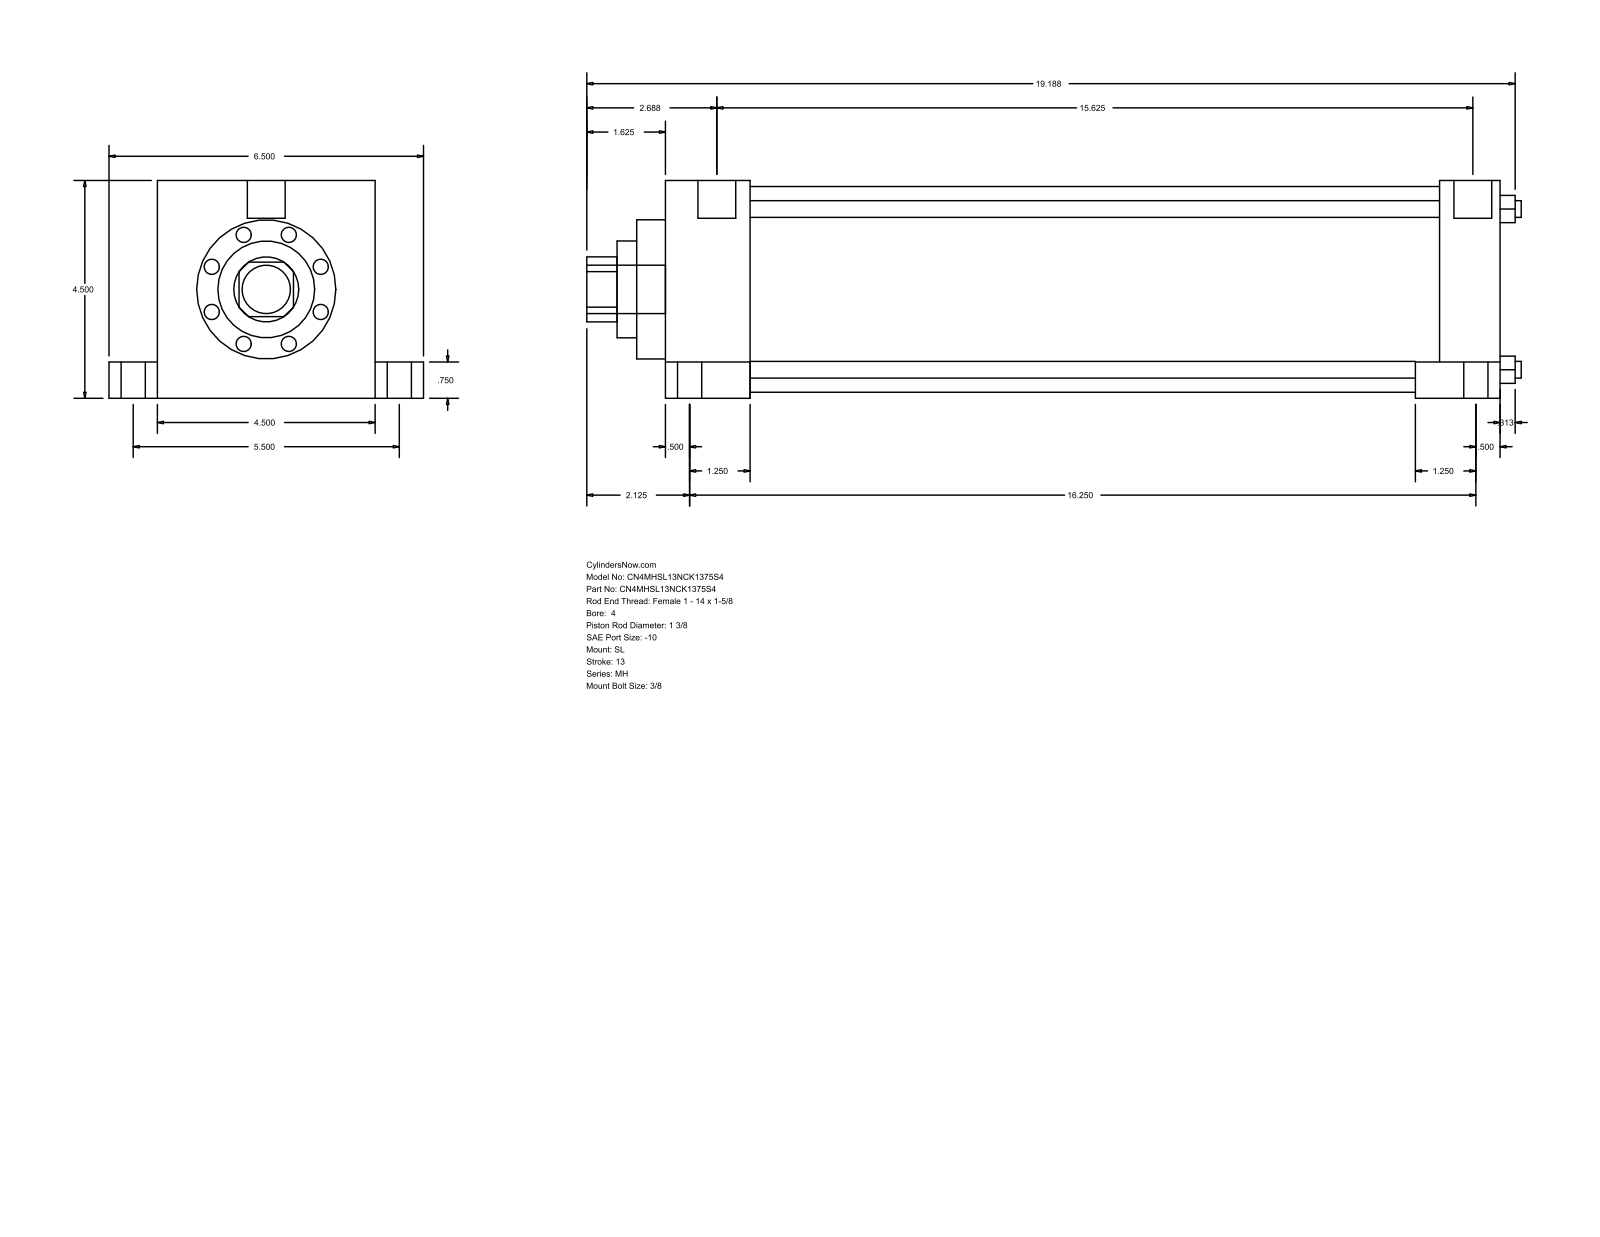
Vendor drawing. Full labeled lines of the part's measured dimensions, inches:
Part name (STEP PRODUCT): MH_SL__0400_1.375
STEP written by: GSSL Pune (CONFIG_CONTROL_DESIGN)
Units: inches
Bodies: 0 solids, 110 faces (77 planar, 33 cylindrical, 0 other)
Overall size (bounding box): 19.313 × 6.5 × 4.5
Round holes (diameter × count): ⌀0.345 ×4, ⌀1.375 ×1, ⌀2 ×1, ⌀2.875 ×1, ⌀4.25 ×1
Round bosses / shafts (diameter × count): ⌀0.75 ×4, ⌀0.5 ×4, ⌀0.344 ×4, ⌀0.781 ×2, ⌀1 ×1
Partial cylindrical surfaces — rounded edges, fillets, slot ends (radius × count): R0.672 ×1
Main face-to-face distances: 4.5, 17.25, 1.75, 15.5, 16, 14.25, 1.25, 1, 5.5, 0.75
Hole centre spacings: 2.347, 3.32, 4.695
